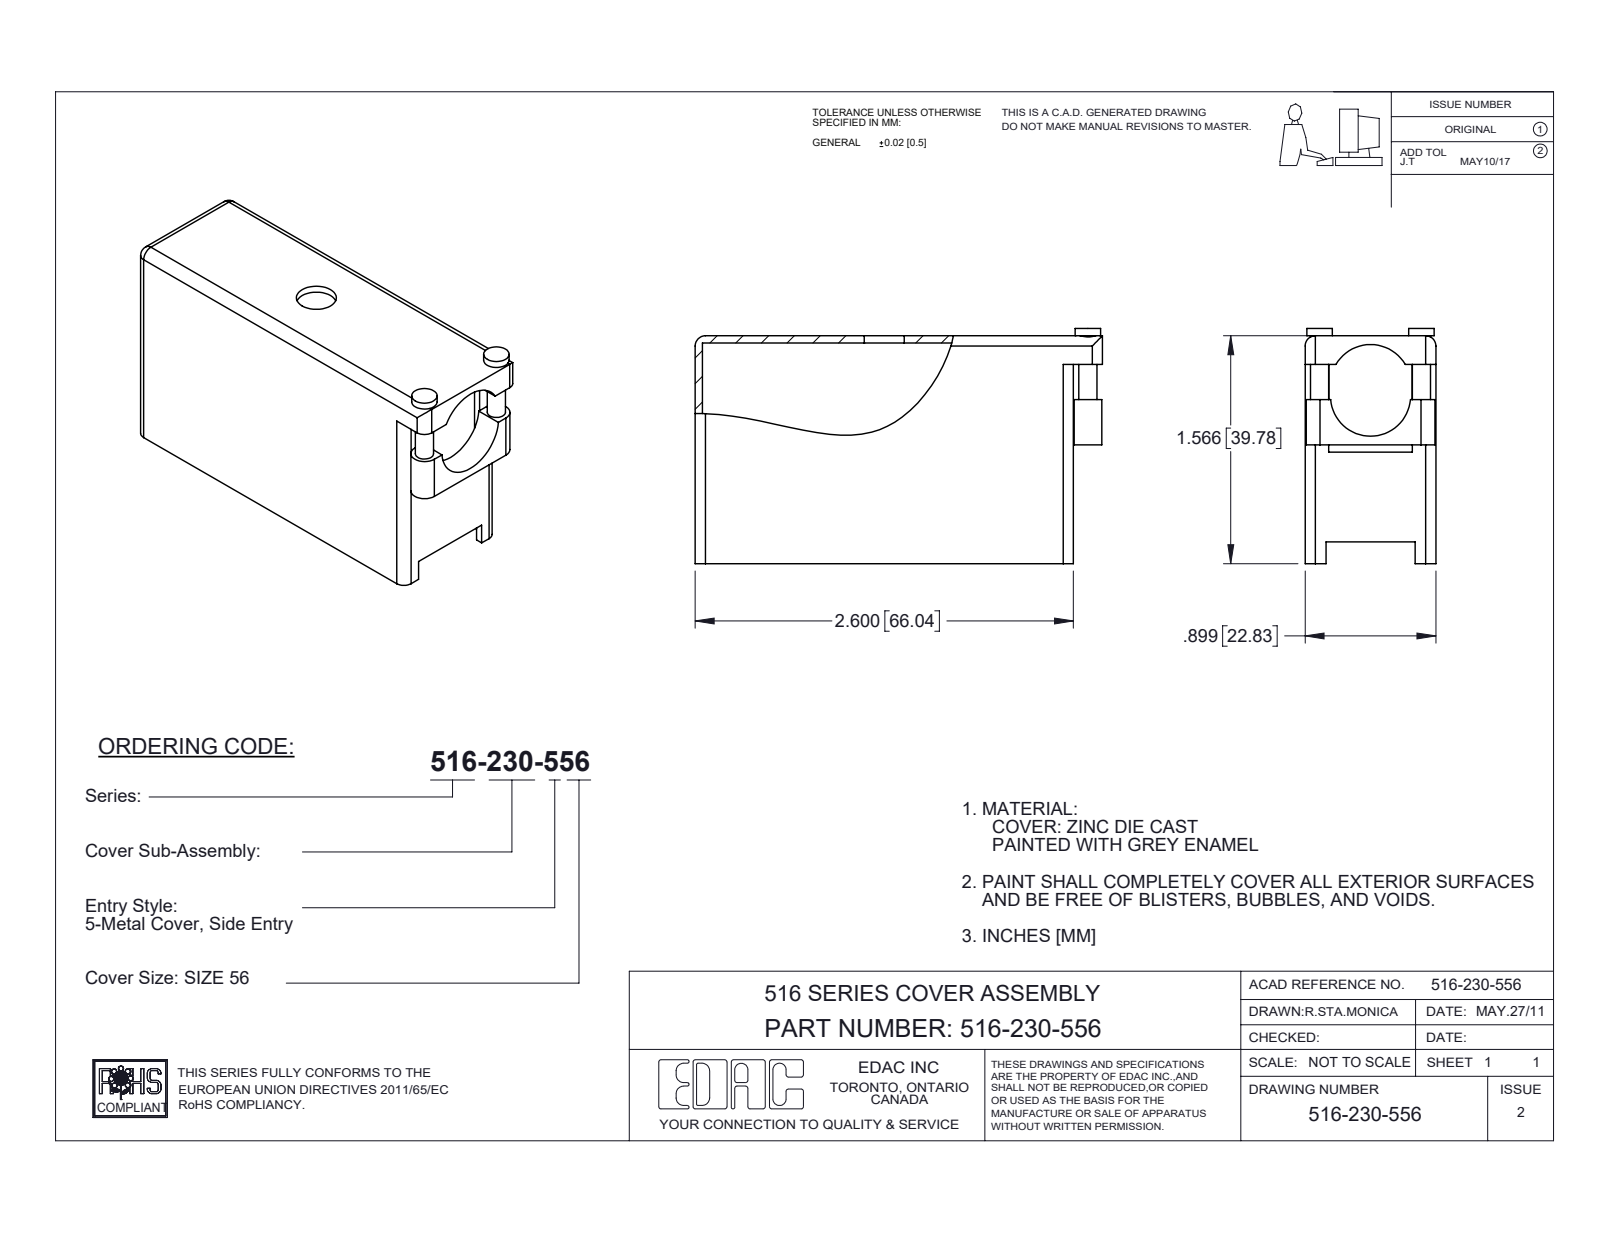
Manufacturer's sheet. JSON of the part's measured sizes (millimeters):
{"part_name": "516-230-001_Metal - 056 Side Entry; 516-230-556", "step_written_by": "SolidWorks 2020 (AUTOMOTIVE_DESIGN)", "units": "millimeters", "bodies": {"solids": 1, "faces": 62, "planar": 33, "cylindrical": 27, "other": 2}, "overall_size": [71.12, 41.05, 22.84], "volume_mm3": 10676, "surface_area_mm2": 16529, "round_holes": [[6.98, 1]], "round_bosses_or_shafts": [[4.45, 2], [3.17, 2]], "partial_cylinders_radius": [[1.78, 9], [2.41, 2], [6.99, 1], [7.01, 1]], "face_to_face_distances": [1.27, 21.56, 20.29, 22.83, 64.77, 63.5, 66.04, 38.51, 39.78, 4.95]}
